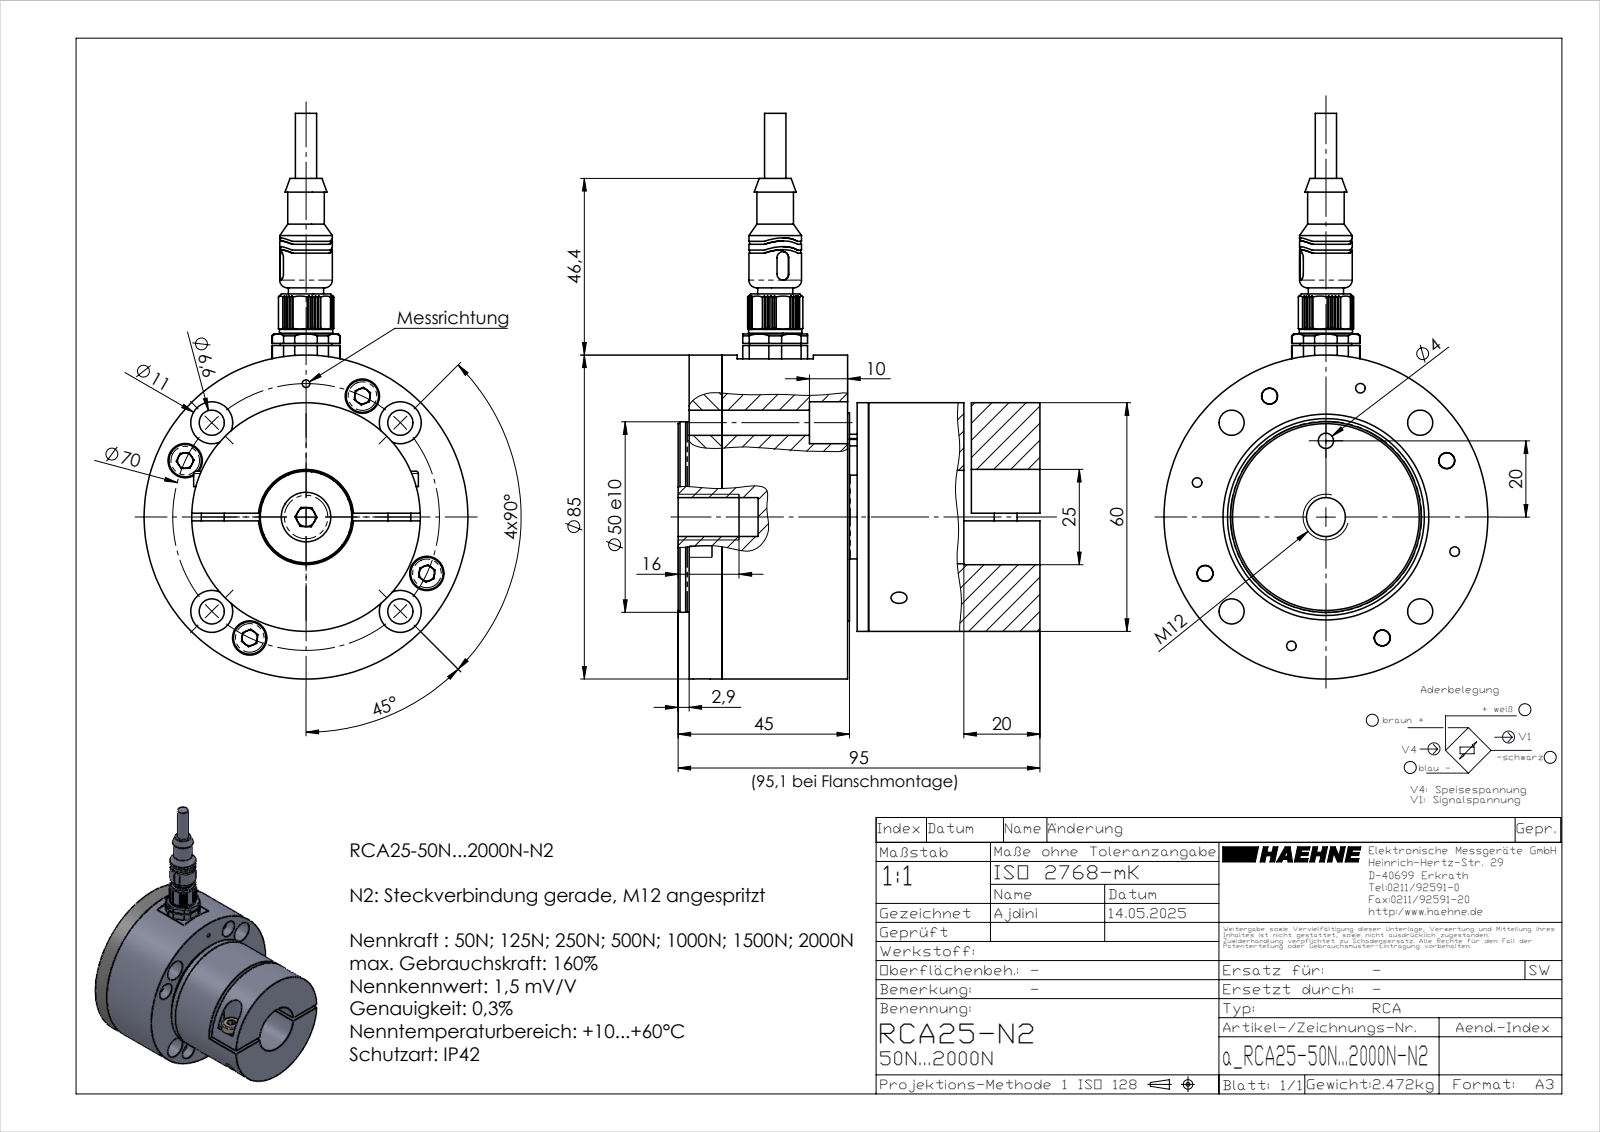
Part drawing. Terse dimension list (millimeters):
name: a_RC-N2 Flanschmontage Scheibe; inafag_1203-tvh_7zkvytp7yxkimpdvw8sj0b5w4_18; inafag_1203-tvh_7zkvytp7yxkimpdvw8sj0b5w4_19; inafag_1203-tvh_7zkvytp7yxkimpdvw8sj0b5w4_08 (+8 more)
written by: SolidWorks 2023 (AUTOMOTIVE_DESIGN)
unit: mm
bodies: 53 solids, 1169 faces (647 planar, 300 cylindrical, 222 other)
size: 148.43 × 95.1 × 85
volume: 365 257 mm³; area: 112 598 mm²
holes: 9× ⌀3.4, 8× ⌀2.5, 6× ⌀6.6, 5× ⌀4.2, 5× ⌀11, 4× ⌀1.1, 4× ⌀1.15, 4× ⌀1.6, 4× ⌀1.85, 4× ⌀4, 4× ⌀5.3, 4× ⌀9
bosses: 9× ⌀3, 8× ⌀5.7, 4× ⌀8.5, 4× ⌀5, 4× ⌀1.8, 4× ⌀1.55, 4× ⌀1.5, 4× ⌀1
rounds: 16× R0.2, 9× R0.3, 4× R0.4, 4× R0.53, 4× R1, 4× R1.27, 4× R12, 2× R1.6
face distances: 3, 2, 8.6, 47.1, 45, 11.6, 50, 30, 35.5, 50.1
hole spacings: 35, 49.5, 24.78, 25.2, 32.8, 51.14, 56.46, 2.5
